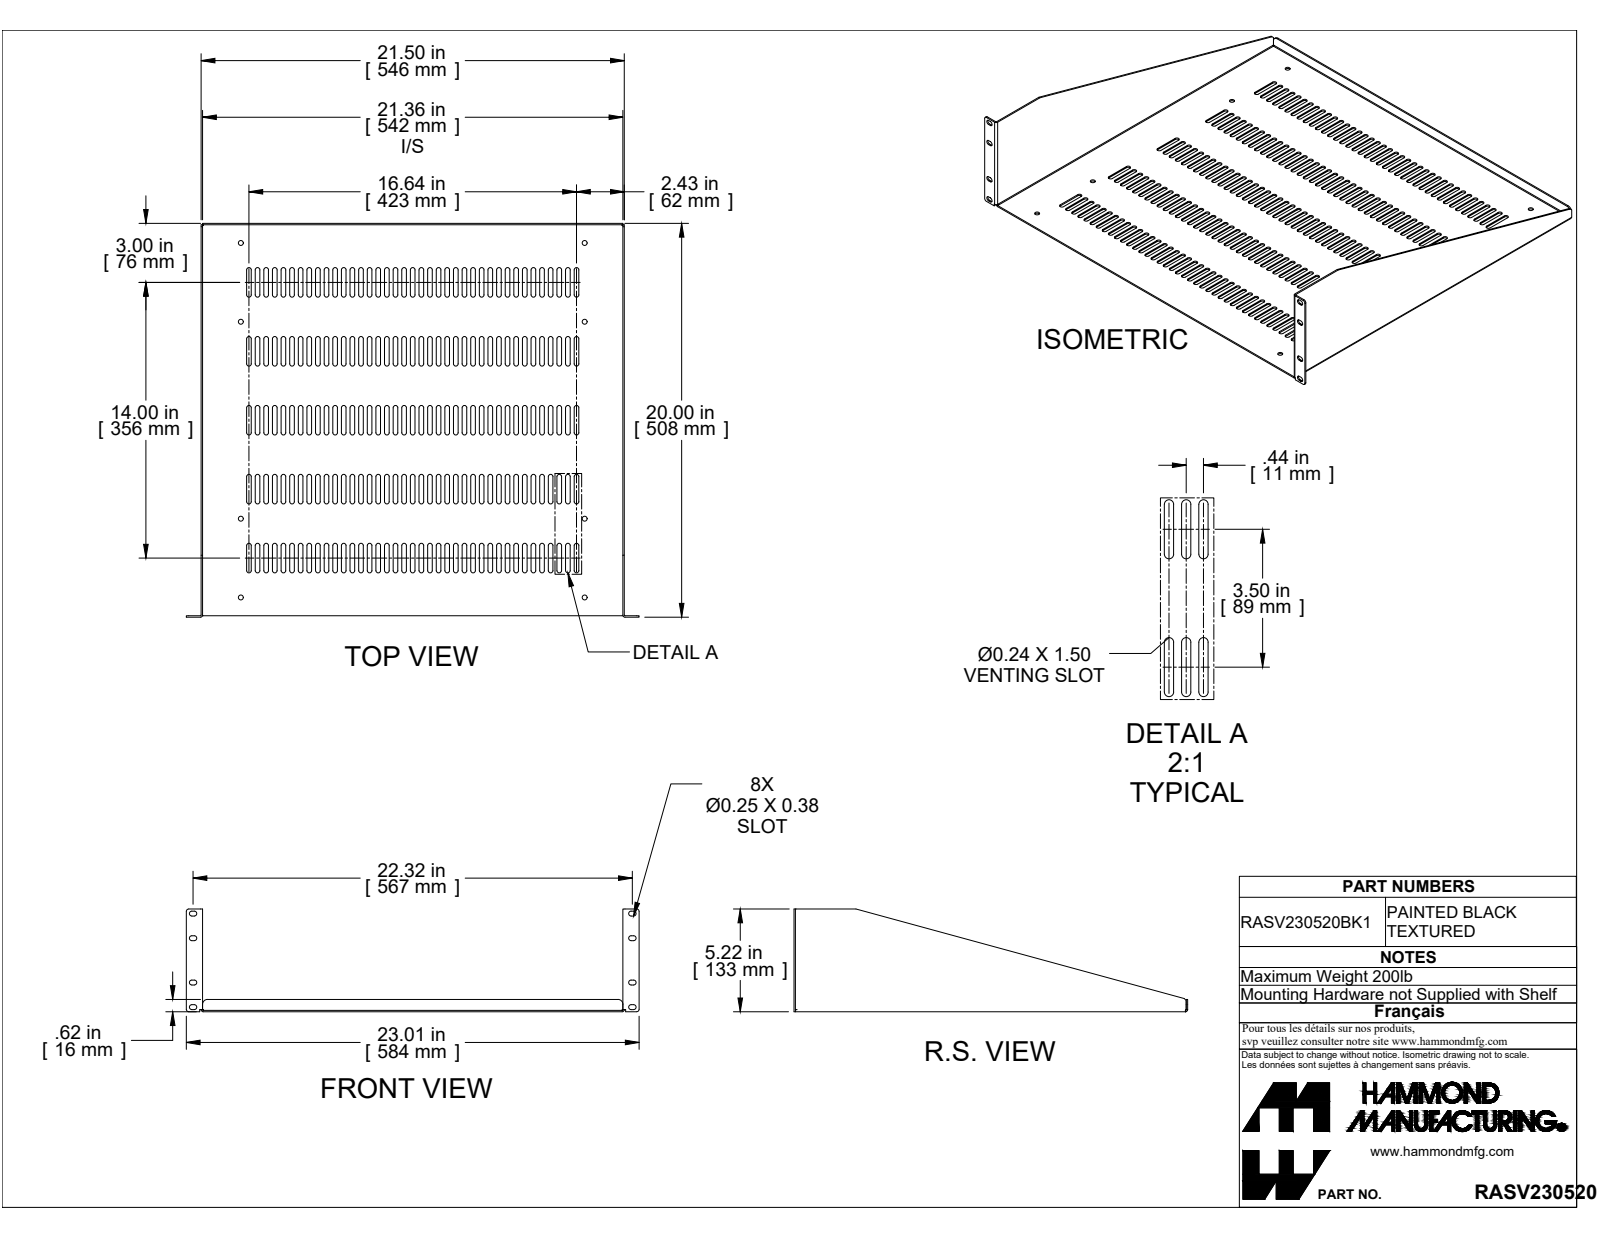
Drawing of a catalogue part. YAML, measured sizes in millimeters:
part_name: "RASV230520BK1"
step_written_by: "SolidWorks 2019 (CONFIG_CONTROL_DESIGN)"
units: millimeters
bodies: {solids: 1, faces: 884, planar: 446, cylindrical: 434, other: 4}
overall_size: [584.4, 508, 132.5]
volume: 597800
surface_area: 689000
round_holes:
  - {diameter: 6.4, count: 8}
partial_cylinders:
  - {radius: 3, count: 370}
  - {radius: 3, count: 20}
  - {radius: 3.2, count: 20}
  - {radius: 0.9, count: 5}
  - {radius: 2.7, count: 5}
  - {radius: 1.4, count: 3}
  - {radius: 6.4, count: 2}
face_to_face_distances: [1.8, 544.3, 542.4, 546.1, 504.3, 506.2, 1.8, 506.2, 508, 22.3]
hole_center_spacings: [101.6, 355.6, 443.7, 455.2, 568.6, 254, 457.2, 511.3]
